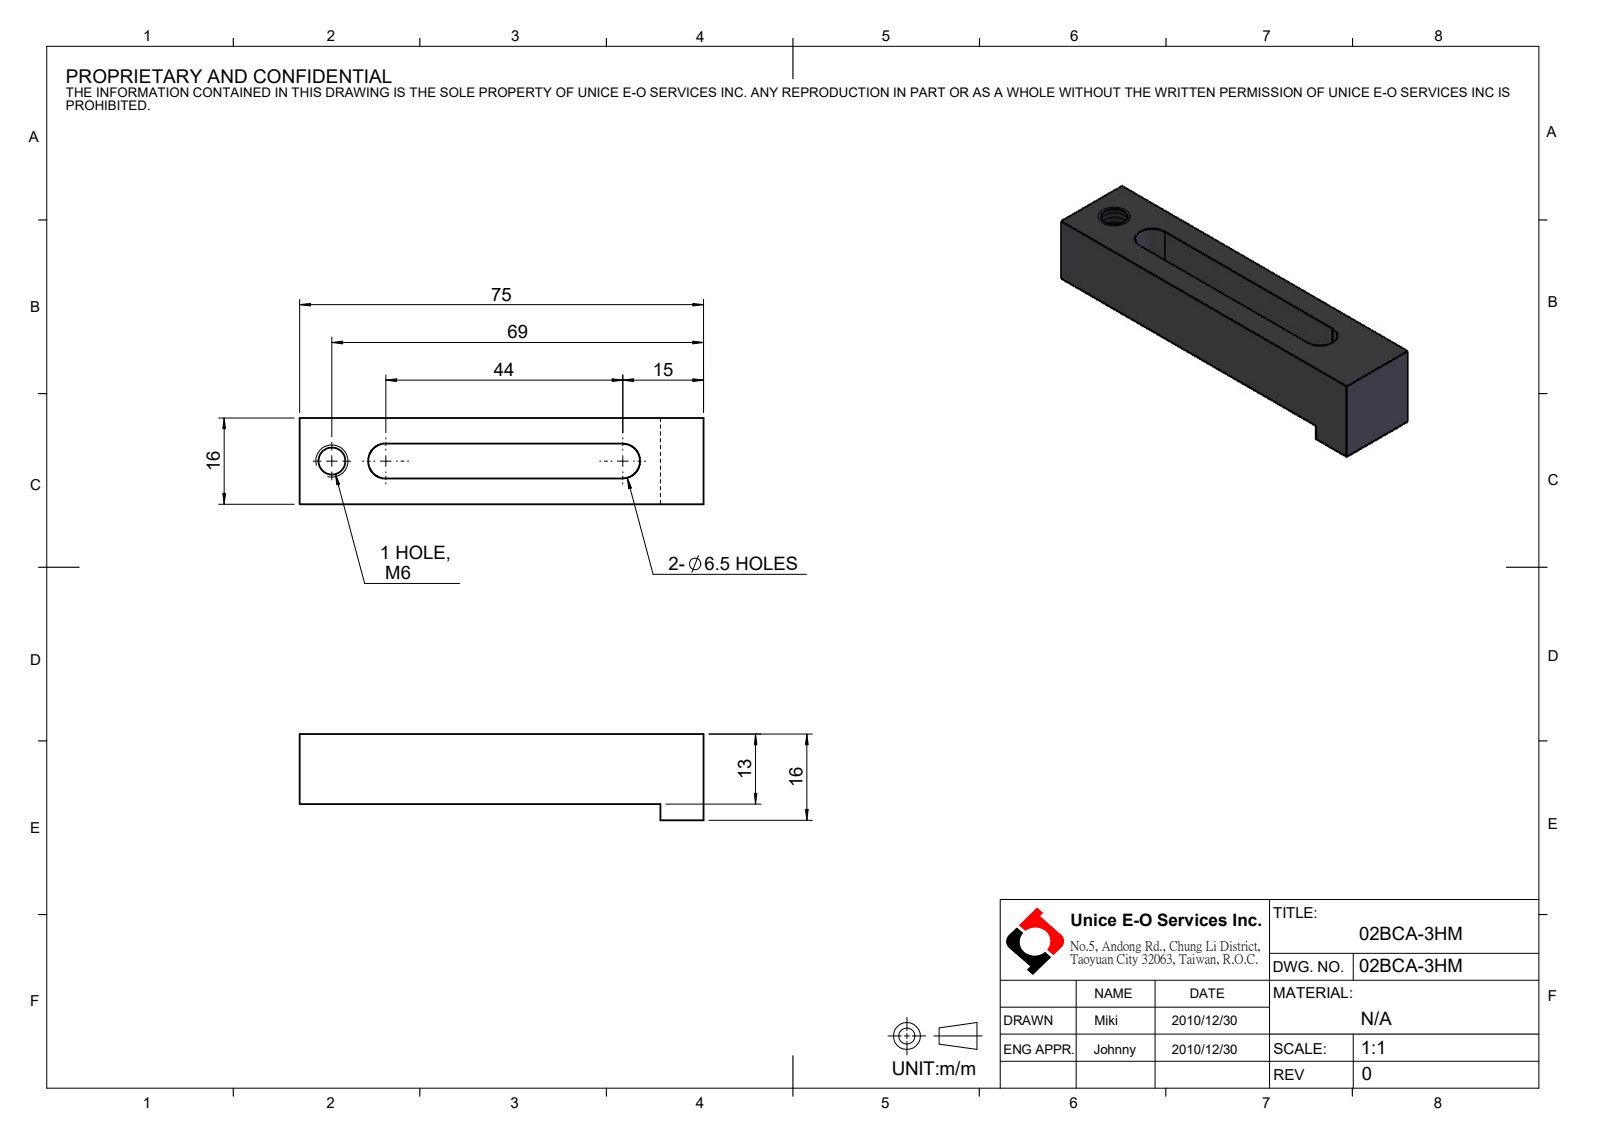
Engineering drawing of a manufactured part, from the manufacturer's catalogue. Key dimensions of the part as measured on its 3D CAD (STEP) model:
Part name (STEP PRODUCT): U-F1-02BCA3HM1-D0
STEP written by: SolidWorks 2016 (CONFIG_CONTROL_DESIGN)
Units: millimetres
Bodies: 1 solid, 14 faces (10 planar, 4 cylindrical, 0 other)
Overall size (bounding box): 75 × 16 × 16
Volume: 11 579 mm³ · Surface area: 5 846 mm²
Round holes (diameter × count): ⌀5 ×1
Partial cylindrical surfaces — rounded edges, fillets, slot ends (radius × count): R3.25 ×2
Main face-to-face distances: 4.75, 11.25, 16, 13, 6.5, 75, 3, 67, 8
